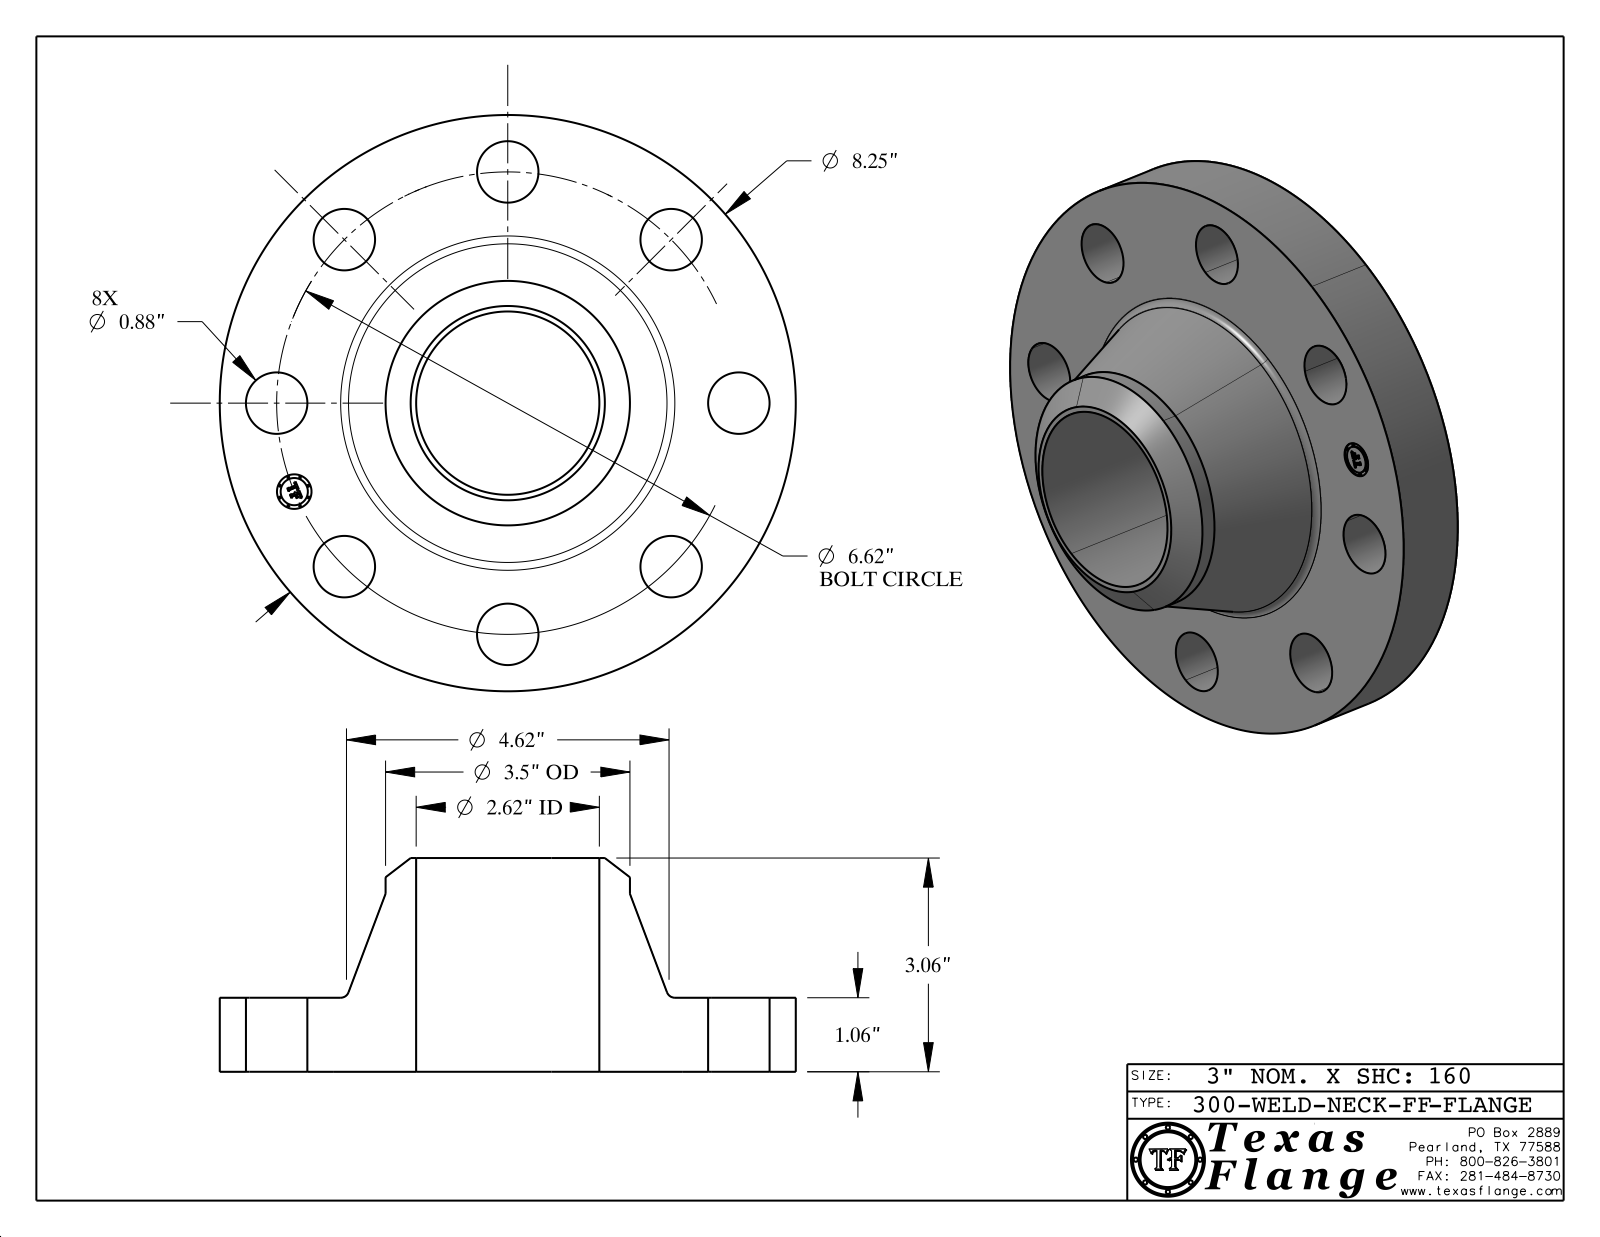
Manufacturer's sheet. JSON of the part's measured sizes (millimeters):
{"part_name": "300-WELD-NECK-FF", "step_written_by": "CATIA V5 STEP AP214 (AUTOMOTIVE_DESIGN)", "units": "millimeters", "bodies": {"solids": 1, "faces": 417, "planar": 369, "cylindrical": 42, "other": 6}, "overall_size": [209.6, 209.6, 77.7], "volume_mm3": 963200, "surface_area_mm2": 115500, "round_holes": [[22.4, 8], [12.6, 1], [66.6, 1]], "round_bosses_or_shafts": [[0.8, 8], [209.6, 1], [88.9, 1], [9.9, 1]], "face_to_face_distances": [26.9, 77.7, 50.8, 0.4, 26.5, 51.2, 3.8, 3.7, 0.7, 2.4], "hole_center_spacings": [84.1, 64.3, 155.3, 118.9, 118.9, 32.8, 93.4, 164.9]}
